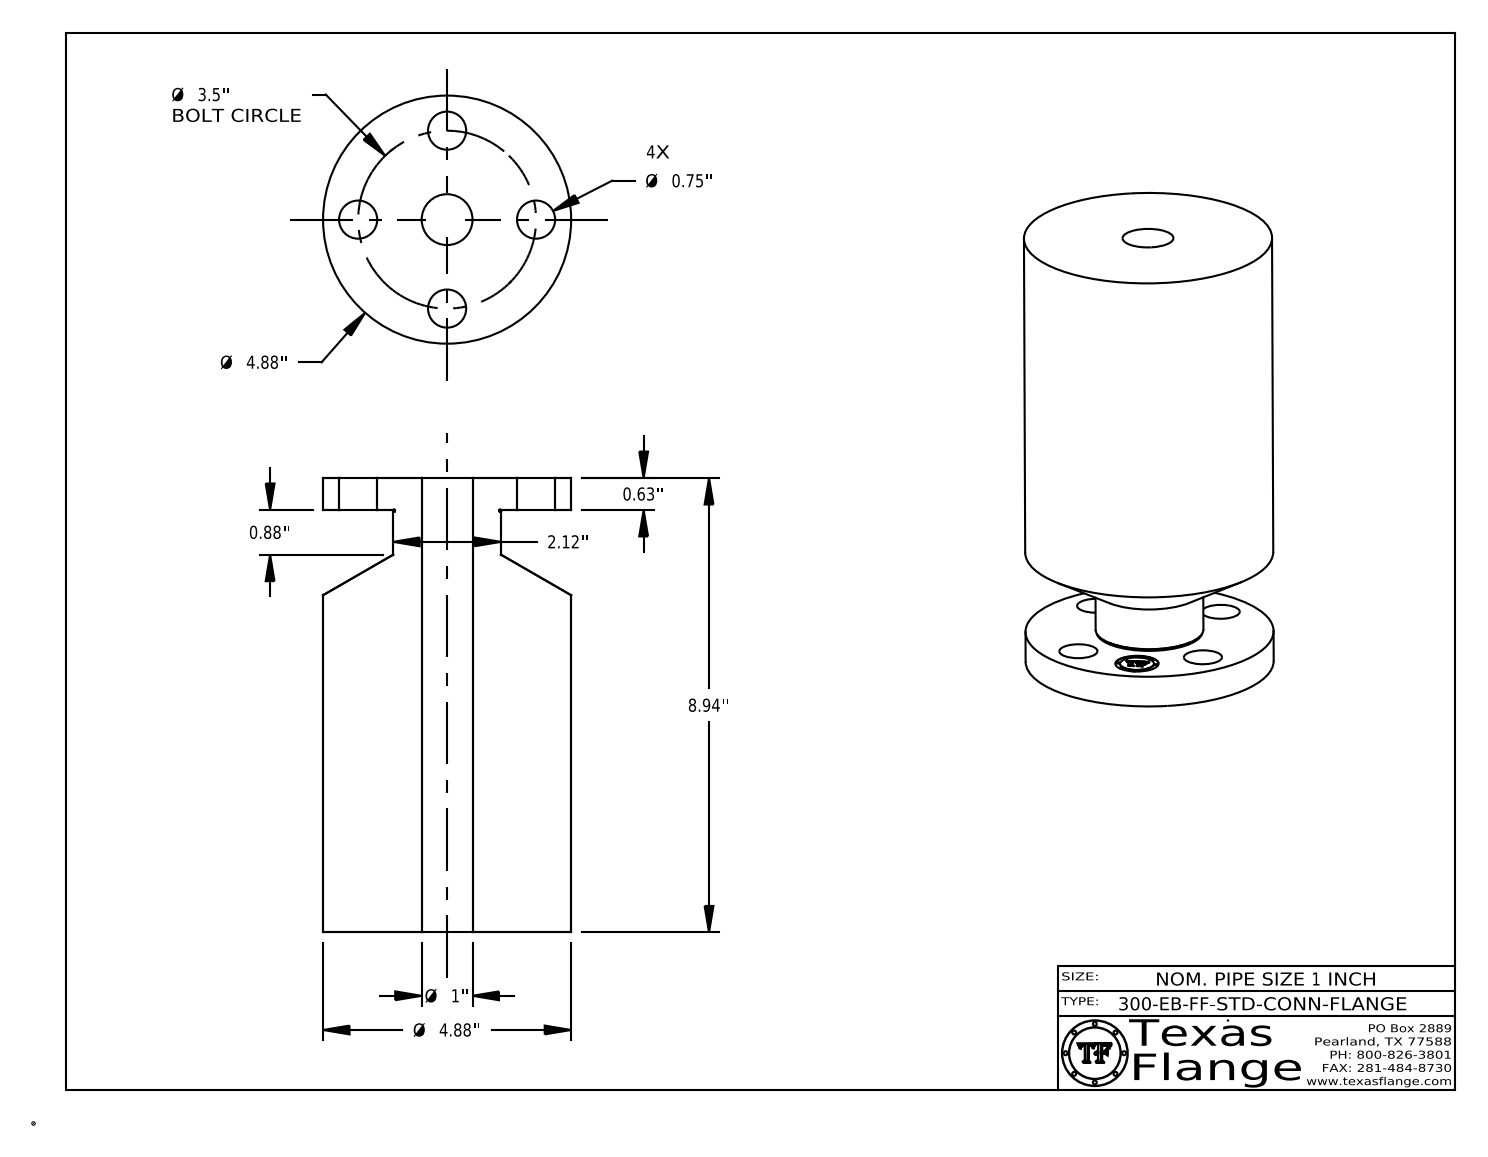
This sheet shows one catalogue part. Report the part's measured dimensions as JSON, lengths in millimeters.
{"part_name": "1-300-EB-FF-STD-CONN-FLANGE", "step_written_by": "CATIA V5 STEP AP214 (AUTOMOTIVE_DESIGN)", "units": "millimeters", "bodies": {"solids": 1, "faces": 410, "planar": 368, "cylindrical": 36, "other": 6}, "overall_size": [227, 124, 124], "volume_mm3": 2275000, "surface_area_mm2": 139700, "round_holes": [[19.1, 4], [21.6, 1], [25.4, 1]], "round_bosses_or_shafts": [[1.3, 8], [124, 1], [53.8, 1], [17, 1]], "face_to_face_distances": [227, 16, 211.1, 15.8, 211.2, 0.4, 6.5, 6.3, 1.2, 4.2], "hole_center_spacings": [44.5, 62.9, 34, 82.1, 88.9]}
